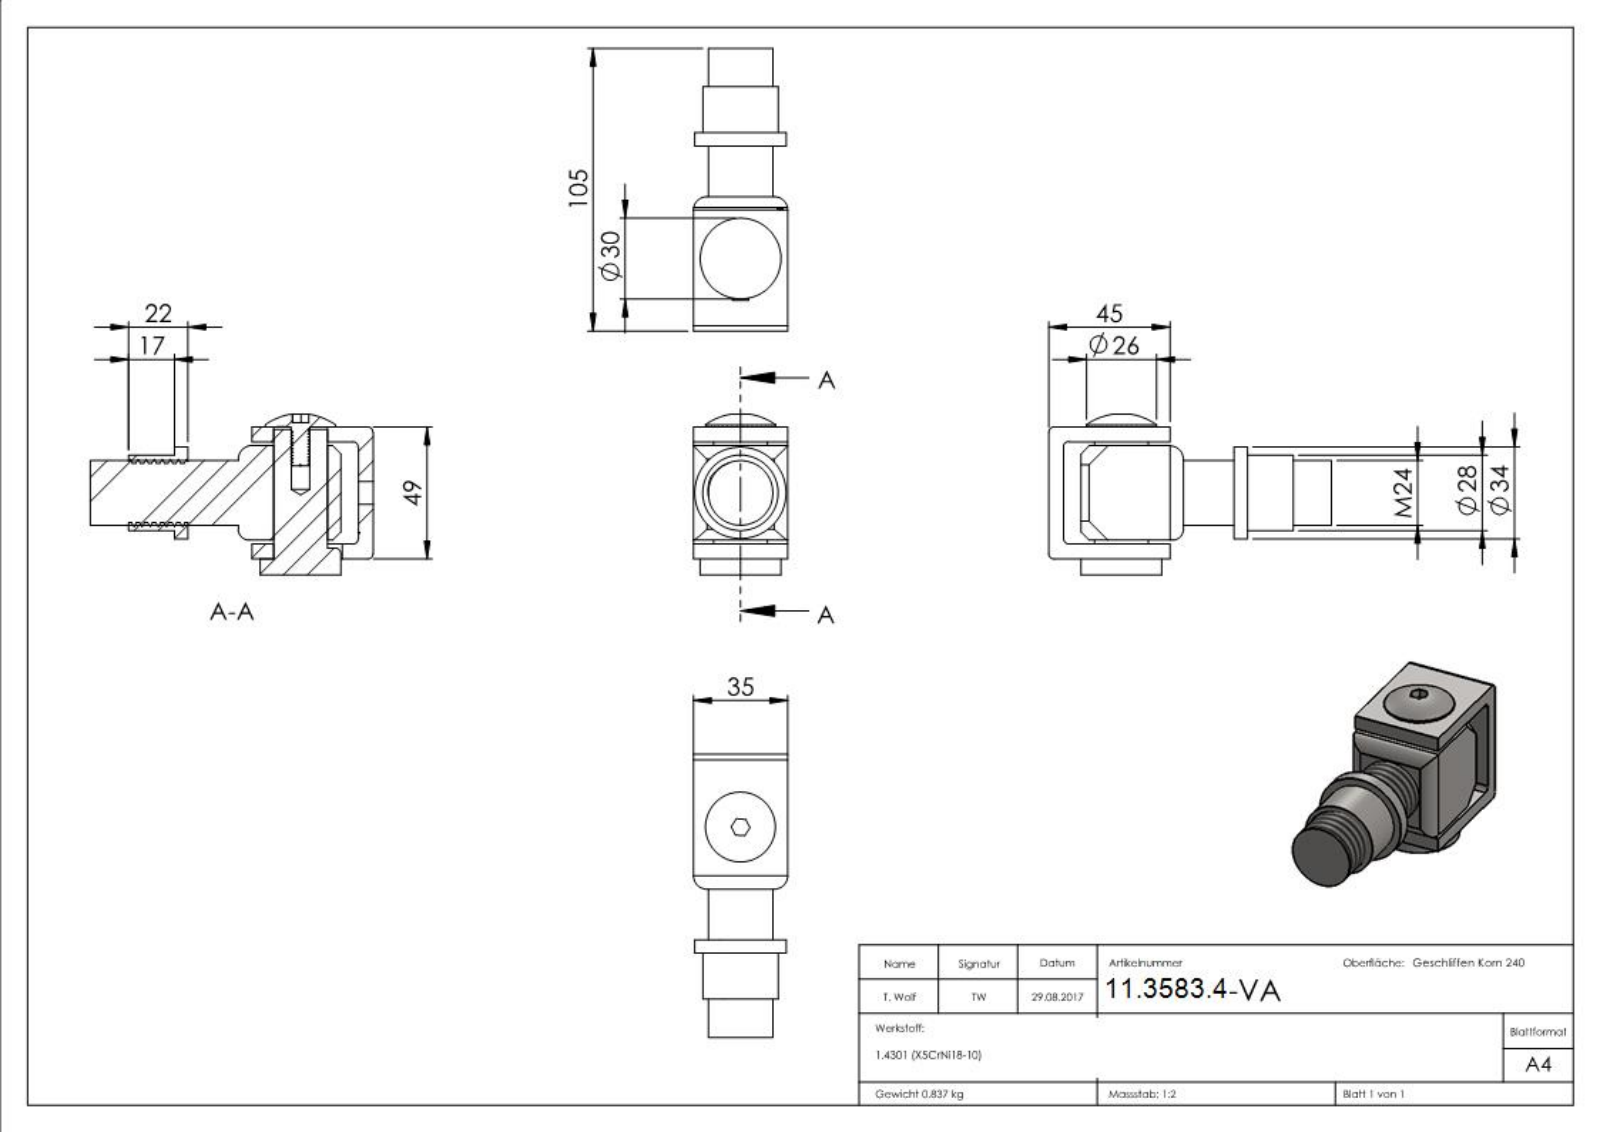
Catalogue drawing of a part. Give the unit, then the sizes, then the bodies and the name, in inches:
Units: inches
Overall size (bounding box): 3.937 × 2.269 × 1.437
Round holes (diameter × count): ⌀0.827 ×2, ⌀0.335 ×1, ⌀0.402 ×1, ⌀0.472 ×1, ⌀0.787 ×1
Round bosses / shafts (diameter × count): ⌀1.437 ×1, ⌀1.398 ×1, ⌀1.181 ×1, ⌀1.142 ×1, ⌀0.945 ×1, ⌀0.917 ×1, ⌀0.866 ×1, ⌀0.764 ×1
Partial cylindrical surfaces — rounded edges, fillets, slot ends (radius × count): R0.02 ×2, R0.079 ×2, R0.217 ×2, R0.118 ×1, R0.787 ×1
Main face-to-face distances: 0.197, 1.673, 1.87, 0.098, 1.28, 0.079, 1.594, 0.276, 1.476, 1.181
Hole centre spacings: 0.03
Volume: 5.944 in³ · Surface area: 54.44 in²
Bodies: 6 solids, 310 faces (196 planar, 28 cylindrical, 86 other)
Part name (STEP PRODUCT): 120-M24-VA Teil6_120-M24-VA Teil6; 120-M24-VA Teil1_120-M24-VA Teil1; 120-M24-VA Teil3; 120-M24-VA Teil5_120-M24-VA Teil5 (+8 more)
STEP written by: SolidWorks 2018 (CONFIG_CONTROL_DESIGN)
